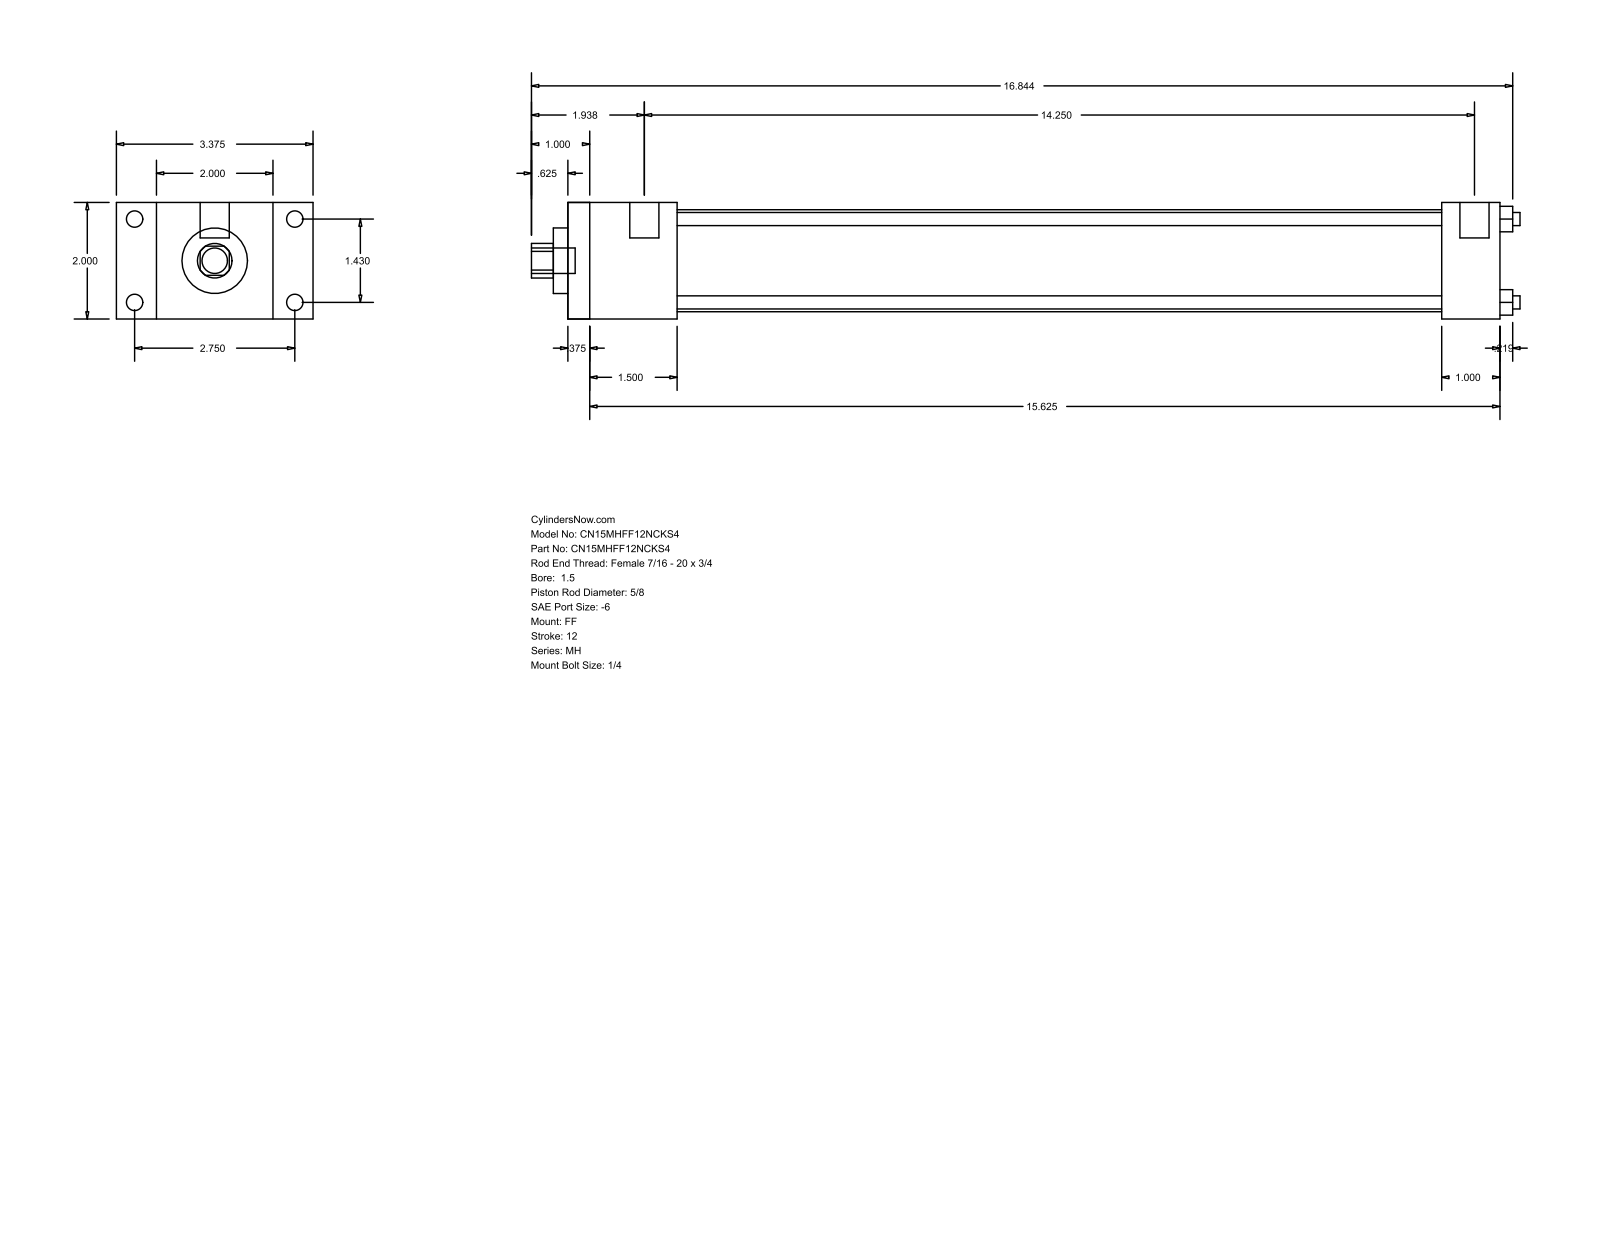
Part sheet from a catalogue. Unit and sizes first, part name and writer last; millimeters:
Units: millimetres
Overall size (bounding box): 431.01 × 85.72 × 50.8
Round holes (diameter × count): ⌀5.71 ×4, ⌀15.88 ×1, ⌀28.57 ×1, ⌀44.45 ×1
Round bosses / shafts (diameter × count): ⌀7.14 ×4, ⌀5.56 ×4, ⌀12.7 ×2, ⌀11.11 ×1
Partial cylindrical surfaces — rounded edges, fillets, slot ends (radius × count): R7.54 ×1
Main face-to-face distances: 50.8, 406.39, 9.52, 396.87, 17.46, 68.26, 47.62, 38.1, 358.77, 381
Hole centre spacings: 25.68, 36.32, 51.36
Bodies: 0 solids, 92 faces (64 planar, 28 cylindrical, 0 other)
Part name (STEP PRODUCT): MH_FF__0150_0.625
STEP written by: GSSL Pune (CONFIG_CONTROL_DESIGN)
